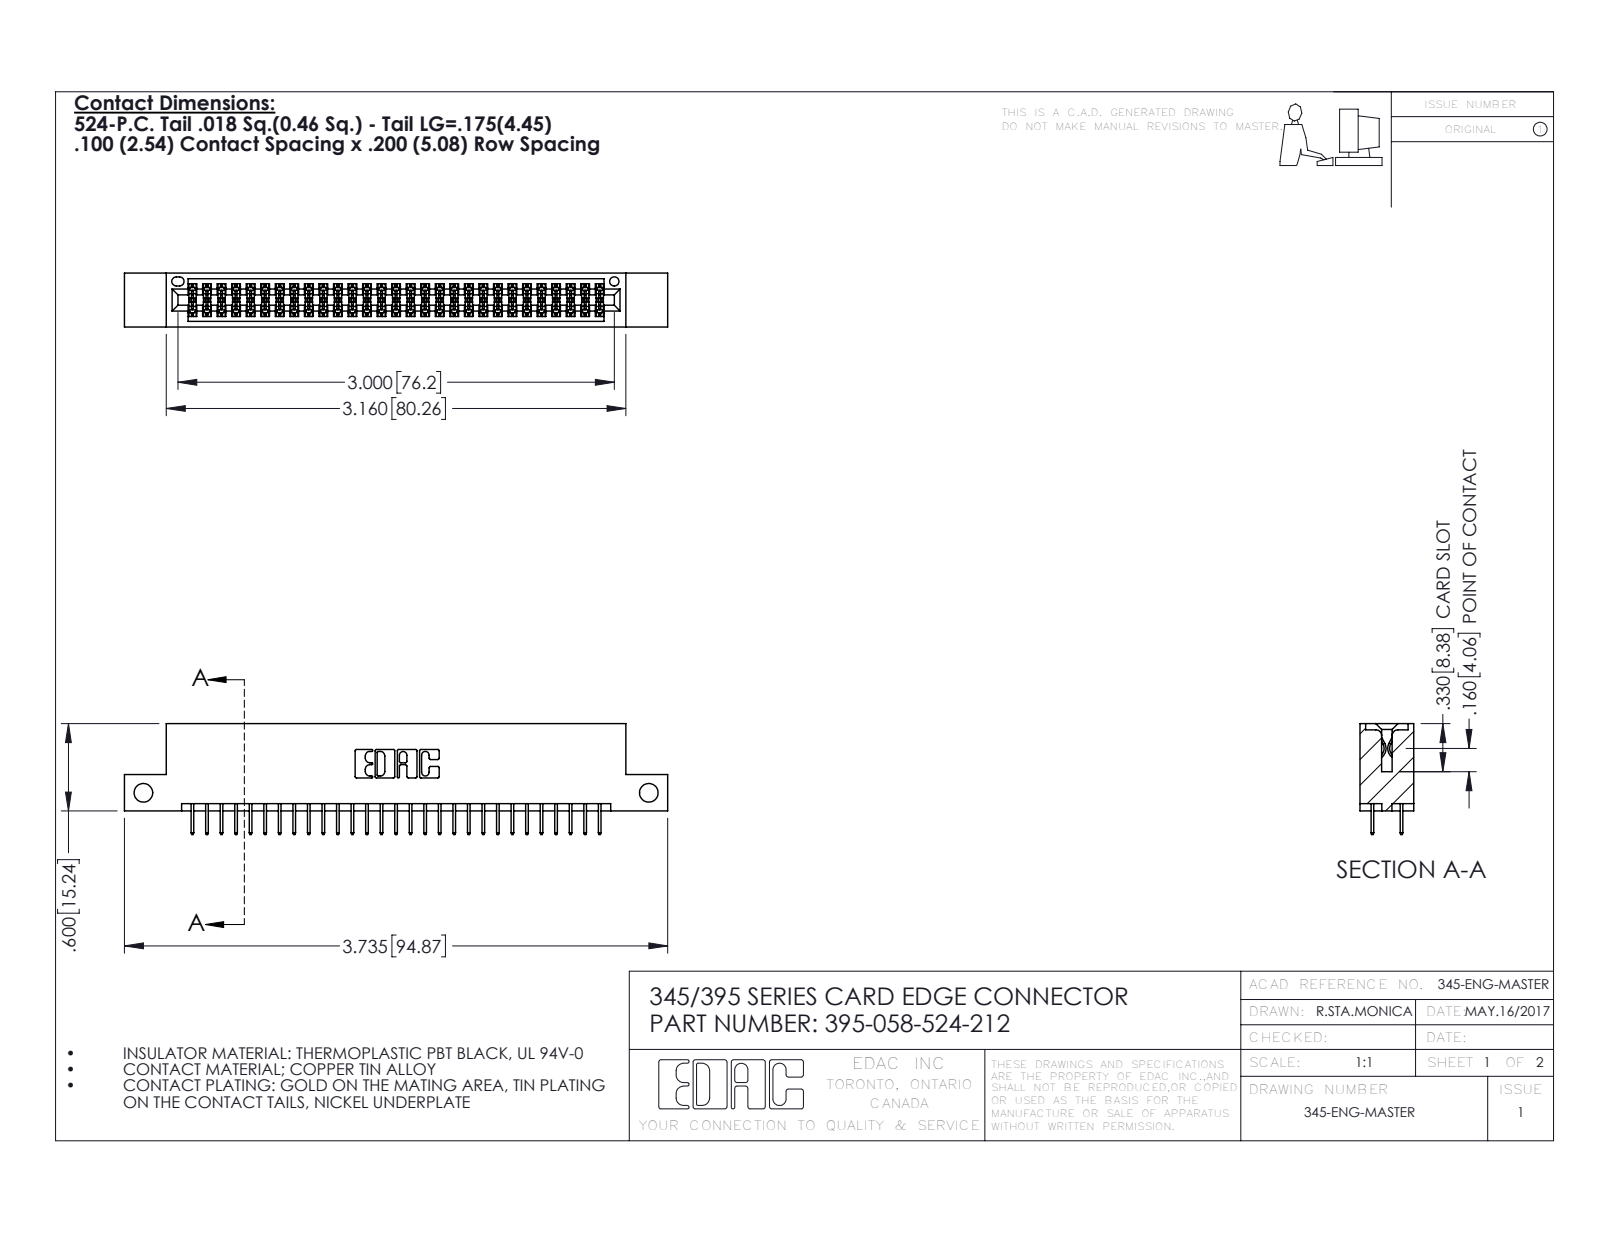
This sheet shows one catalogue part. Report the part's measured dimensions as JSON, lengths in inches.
{"part_name": "345-292-001_345-293-124; 345 Part_Flush Mounting Lugs - Side Mount; 395-058-524-212", "step_written_by": "SolidWorks 2016 (CONFIG_CONTROL_DESIGN)", "units": "inches", "bodies": {"solids": 59, "faces": 3258, "planar": 2342, "cylindrical": 916, "other": 0}, "overall_size": [3.735, 0.762, 0.37], "volume_in3": 0.544, "surface_area_in2": 19.48, "round_holes": [[0.128, 2], [0.064, 1]], "partial_cylinders_radius": [[0.006, 87], [0.01, 22], [0.007, 6], [0.031, 6], [0.026, 3], [0.014, 2], [0.019, 2], [0.022, 2]], "face_to_face_distances": [0.298, 0.072, 0.2, 0.37, 0.098, 0.272, 0.025, 0.225, 0.072, 0.175], "hole_center_spacings": [3.475]}
